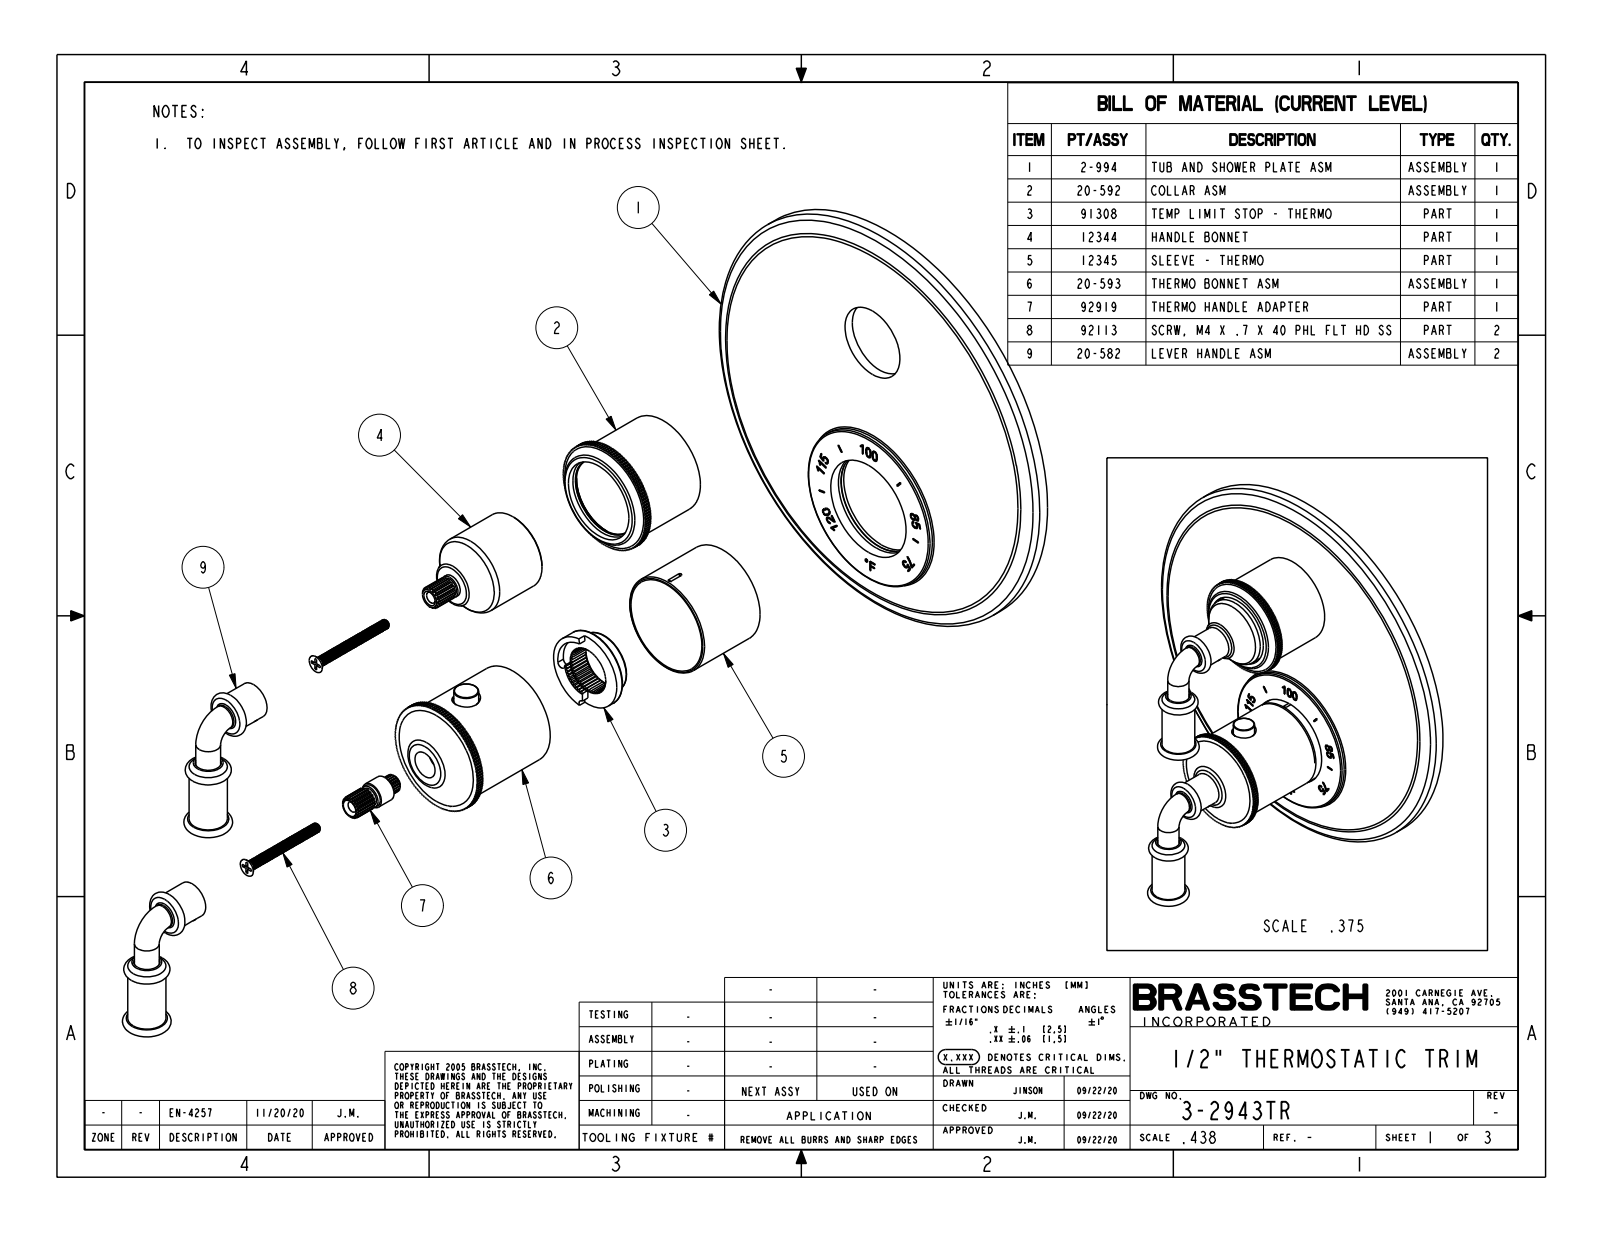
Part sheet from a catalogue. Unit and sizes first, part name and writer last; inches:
Units: inches
Overall size (bounding box): 7.087 × 7.087 × 3.956
Round holes (diameter × count): ⌀0.41 ×2, ⌀0.057 ×1, ⌀0.406 ×1, ⌀0.445 ×1, ⌀1.673 ×1
Round bosses / shafts (diameter × count): ⌀0.39 ×5, ⌀0.6 ×2, ⌀0.595 ×2, ⌀0.37 ×2, ⌀7.087 ×1, ⌀1.654 ×1, ⌀1.654 ×1, ⌀1.65 ×1
Partial cylindrical surfaces — rounded edges, fillets, slot ends (radius × count): R0.915 ×2, R0.039 ×1, R0.793 ×1, R3.522 ×1
Main face-to-face distances: 0.348, 0.438, 0.09, 0.748, 0.25, 0.125, 0.624, 2.283, 1.935, 1.845
Hole centre spacings: 0.257, 1.019, 1.02, 1.699, 1.956
Volume: 22.88 in³ · Surface area: 118.7 in²
Bodies: 1 solid, 1119 faces (598 planar, 283 cylindrical, 238 other)
Part name (STEP PRODUCT): 3-2943TR
STEP written by: CREO PARAMETRIC BY PTC INC, 2019352 (CONFIG_CONTROL_DESIGN)
